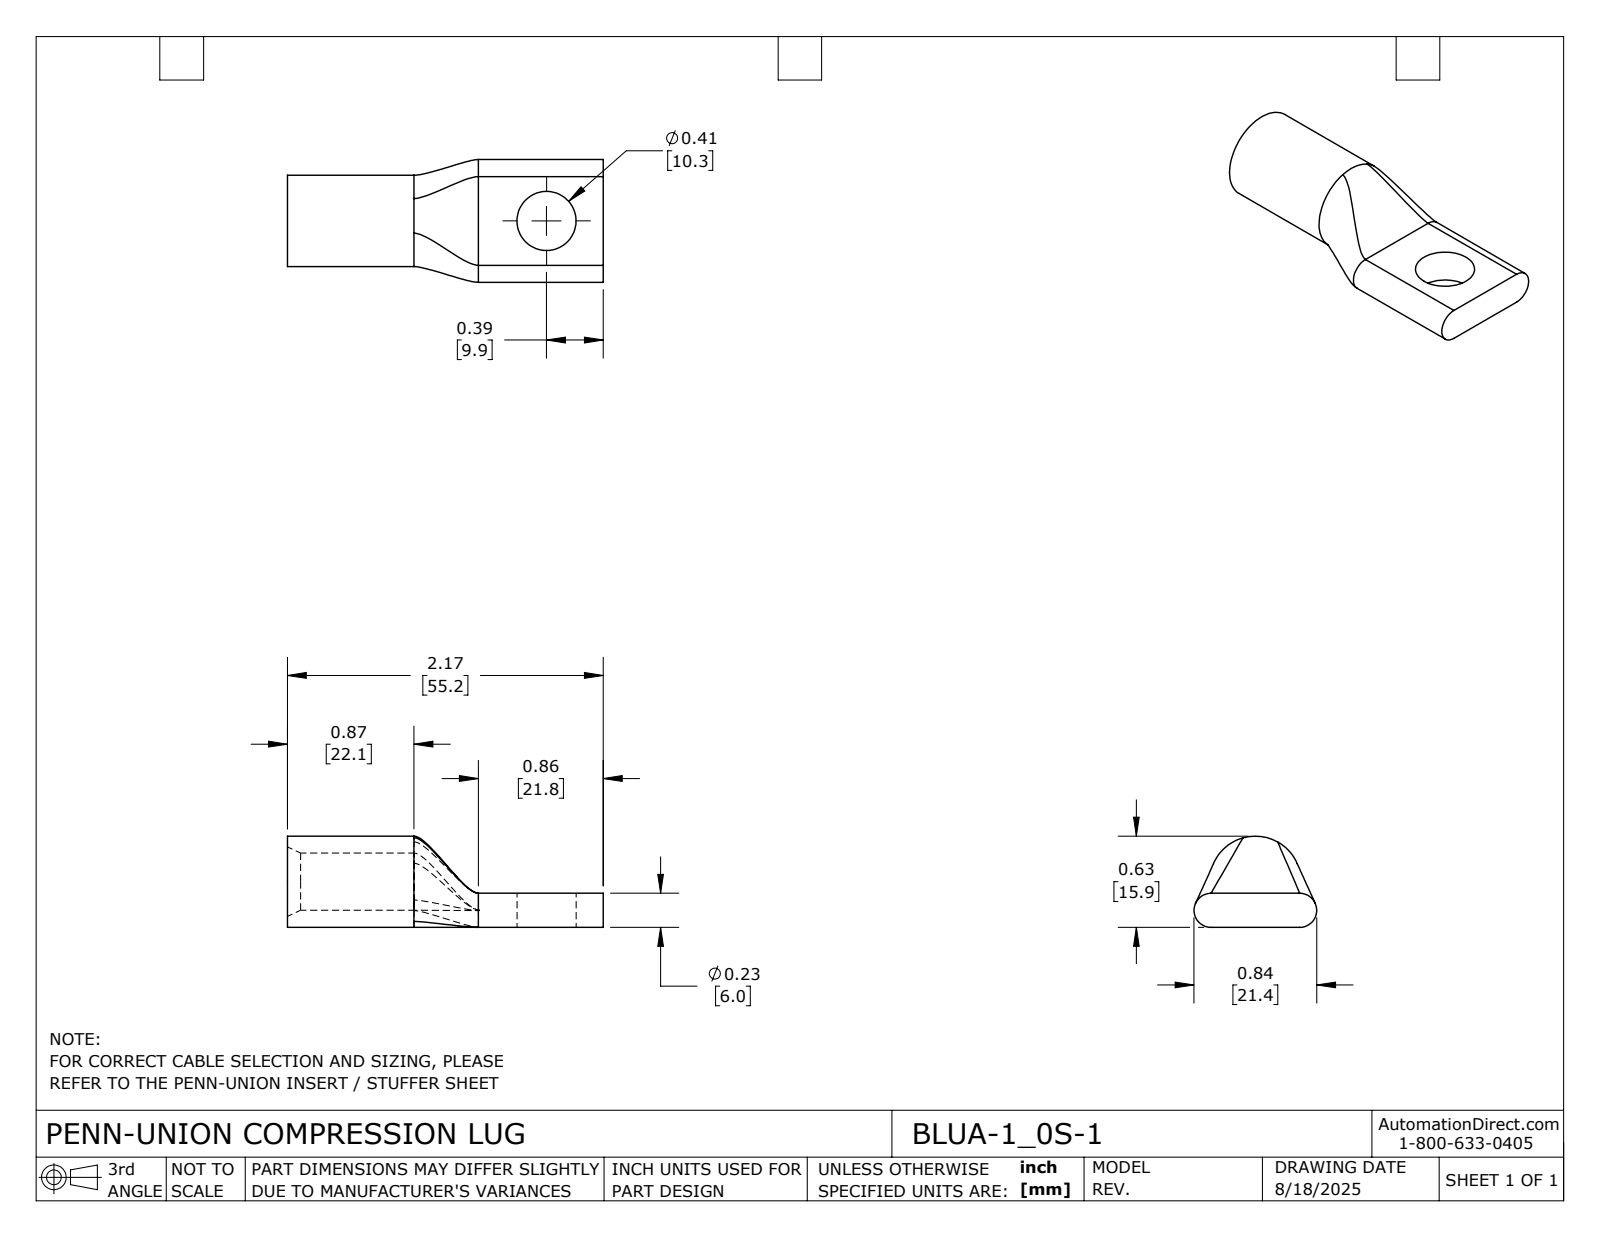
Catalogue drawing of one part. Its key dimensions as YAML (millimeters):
part_name: "BLUA-1_0S-1"
step_written_by: "SolidWorks 2024 (CONFIG_CONTROL_DESIGN)"
units: millimeters
bodies: {solids: 1, faces: 24, planar: 5, cylindrical: 9, other: 10}
overall_size: [55.2, 21.4, 15.9]
volume: 6100
surface_area: 4133
round_holes:
  - {diameter: 10, count: 1}
  - {diameter: 10.3, count: 1}
round_bosses_or_shafts:
  - {diameter: 15.9, count: 1}
partial_cylinders:
  - {radius: 3, count: 2}
face_to_face_distances: [5.9, 55.2, 33.4, 21.8]
